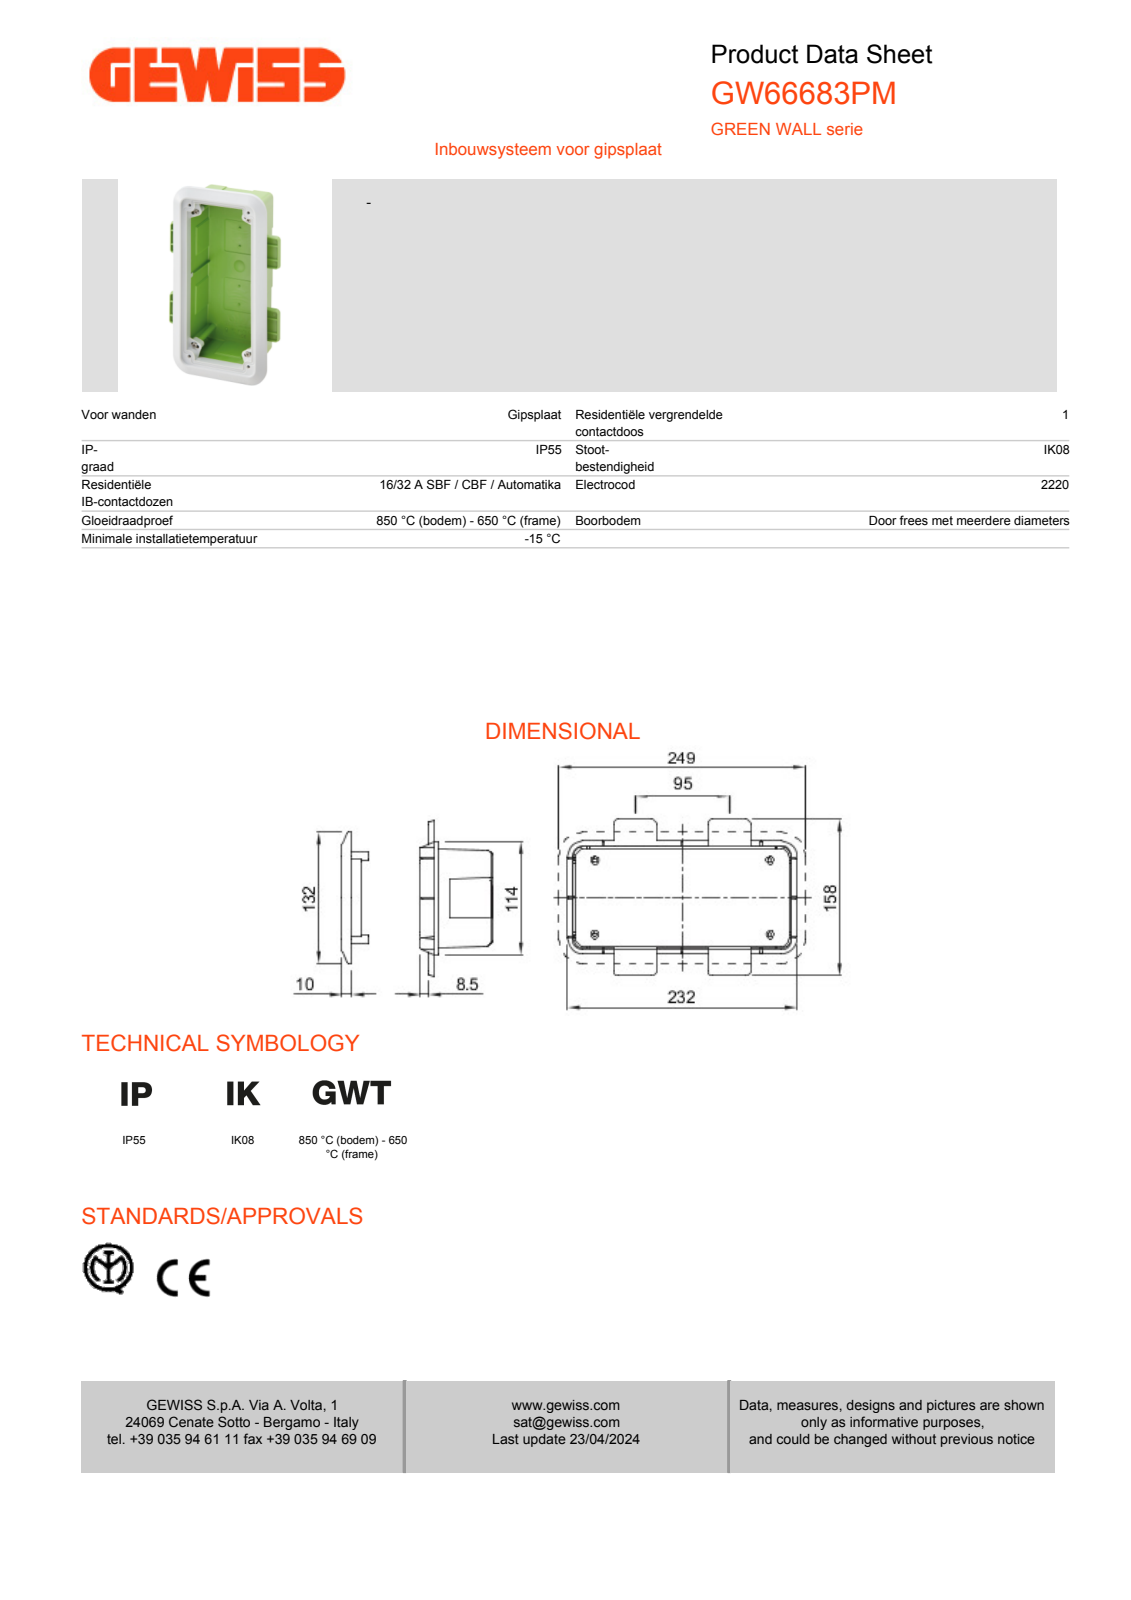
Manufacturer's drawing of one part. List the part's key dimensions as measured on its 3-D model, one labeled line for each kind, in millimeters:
Part name (STEP PRODUCT): 53028833CXXX_SCATOLA_INC_PR_BL; 53025938BXXX_CORNICE_PER_PR_INT; GW66683PM_CASS_PM_PRESE_BL_VR_ASM
STEP written by: CREO PARAMETRIC BY PTC INC, 2019471 (CONFIG_CONTROL_DESIGN)
Units: millimetres
Bodies: 2 solids, 1138 faces (904 planar, 106 cylindrical, 128 other)
Overall size (bounding box): 249 × 157.55 × 82.5
Volume: 226 550 mm³ · Surface area: 237 087 mm²
Round holes (diameter × count): ⌀4.6 ×2, ⌀30 ×1
Round bosses / shafts (diameter × count): ⌀12 ×2
Partial cylindrical surfaces — rounded edges, fillets, slot ends (radius × count): R0.2 ×16, R0.5 ×8, R4.5 ×8, R3 ×4, R3.5 ×4, R7 ×4, R7.7 ×4, R10.5 ×4
Main face-to-face distances: 1.8, 1.79, 14, 2.99, 1.2, 2, 1, 57, 55.2, 1.5
Hole centre spacings: 73.68, 147.36
